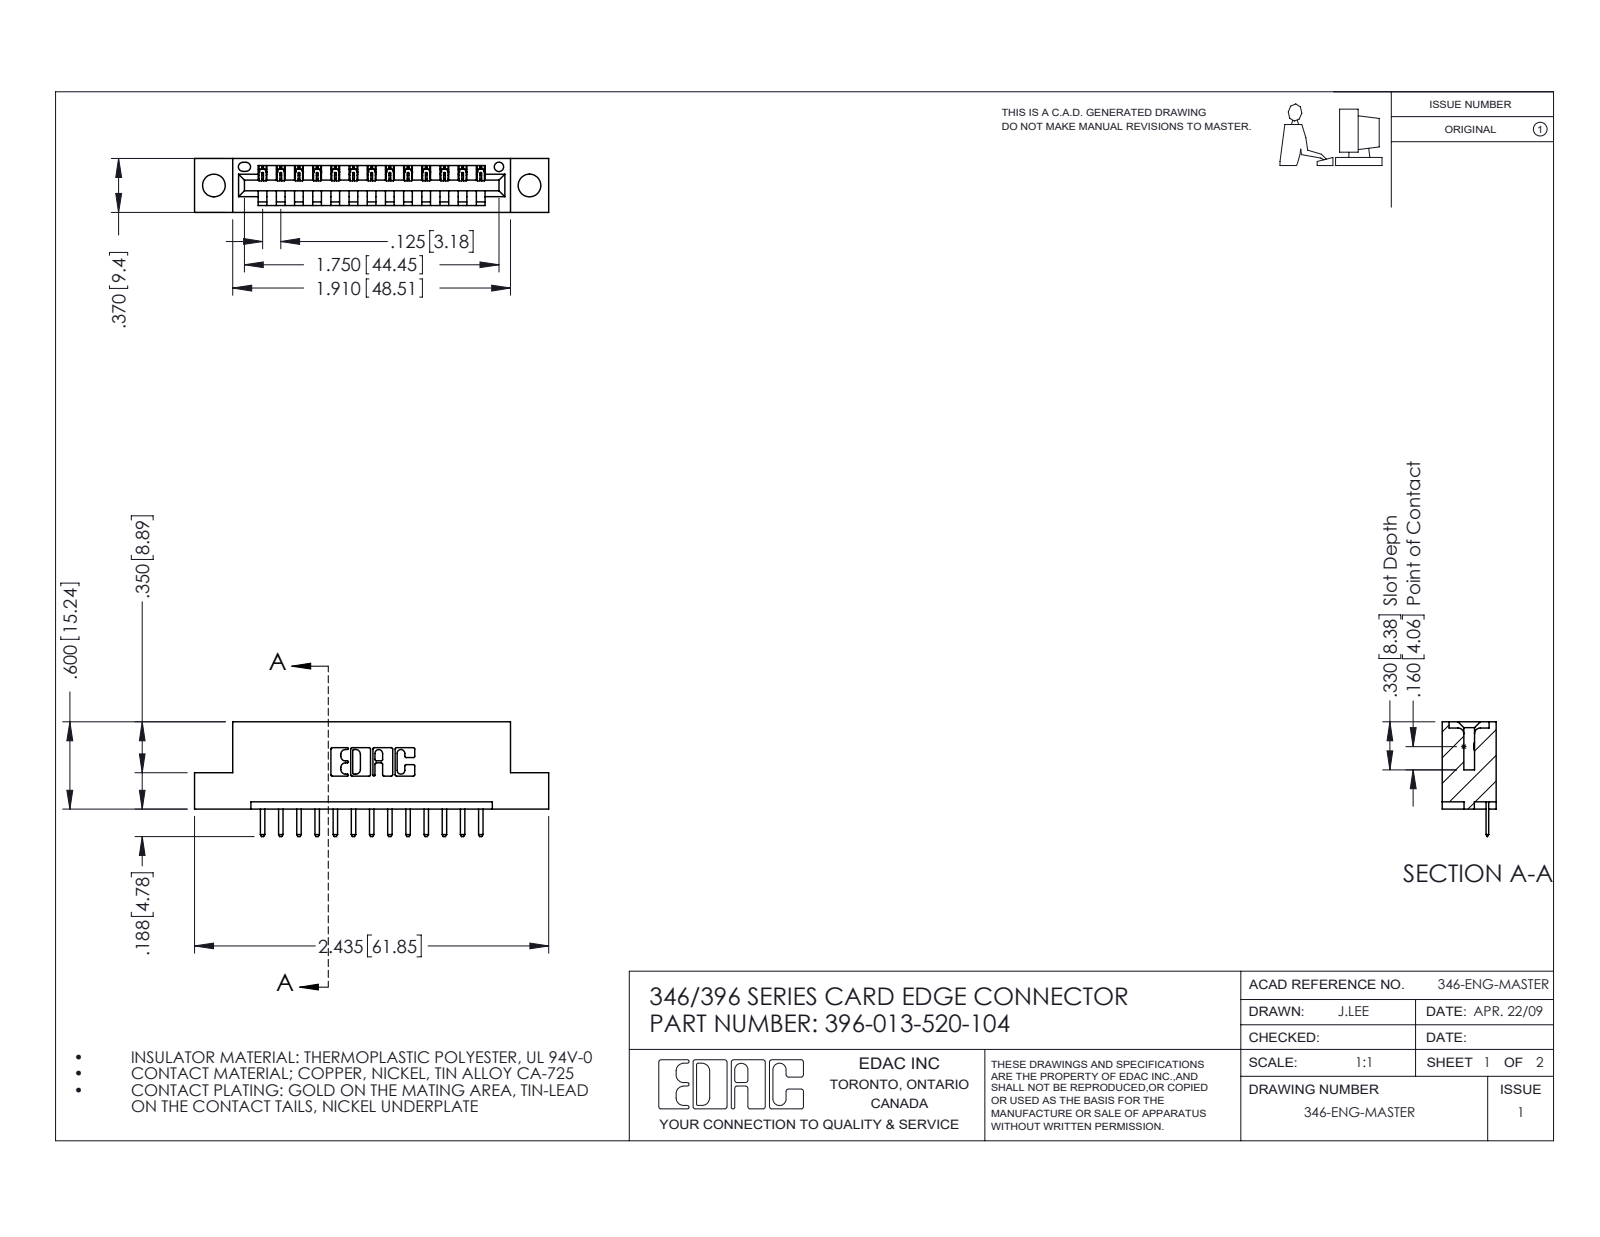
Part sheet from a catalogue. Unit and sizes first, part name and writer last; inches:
Units: inches
Overall size (bounding box): 2.435 × 0.788 × 0.37
Round holes (diameter × count): ⌀0.156 ×2, ⌀0.064 ×1
Partial cylindrical surfaces — rounded edges, fillets, slot ends (radius × count): R0.01 ×28, R0.006 ×26, R0.01 ×22, R0.007 ×6, R0.031 ×6, R0.026 ×3, R0.031 ×2, R0.04 ×2
Main face-to-face distances: 0.25, 0.37, 0.048, 0.322, 0.148, 0.222, 0.1, 0.174, 0.072, 0.298
Hole centre spacings: 0.246, 1.964, 2.17
Volume: 0.341 in³ · Surface area: 9.859 in²
Bodies: 14 solids, 928 faces (622 planar, 306 cylindrical, 0 other)
Part name (STEP PRODUCT): 346 Part_Flush Mounting Lugs - 0.156 Dia-TH; 396-013-520-104; 345-292-001_345-293-120
STEP written by: SolidWorks 2016 (CONFIG_CONTROL_DESIGN)
